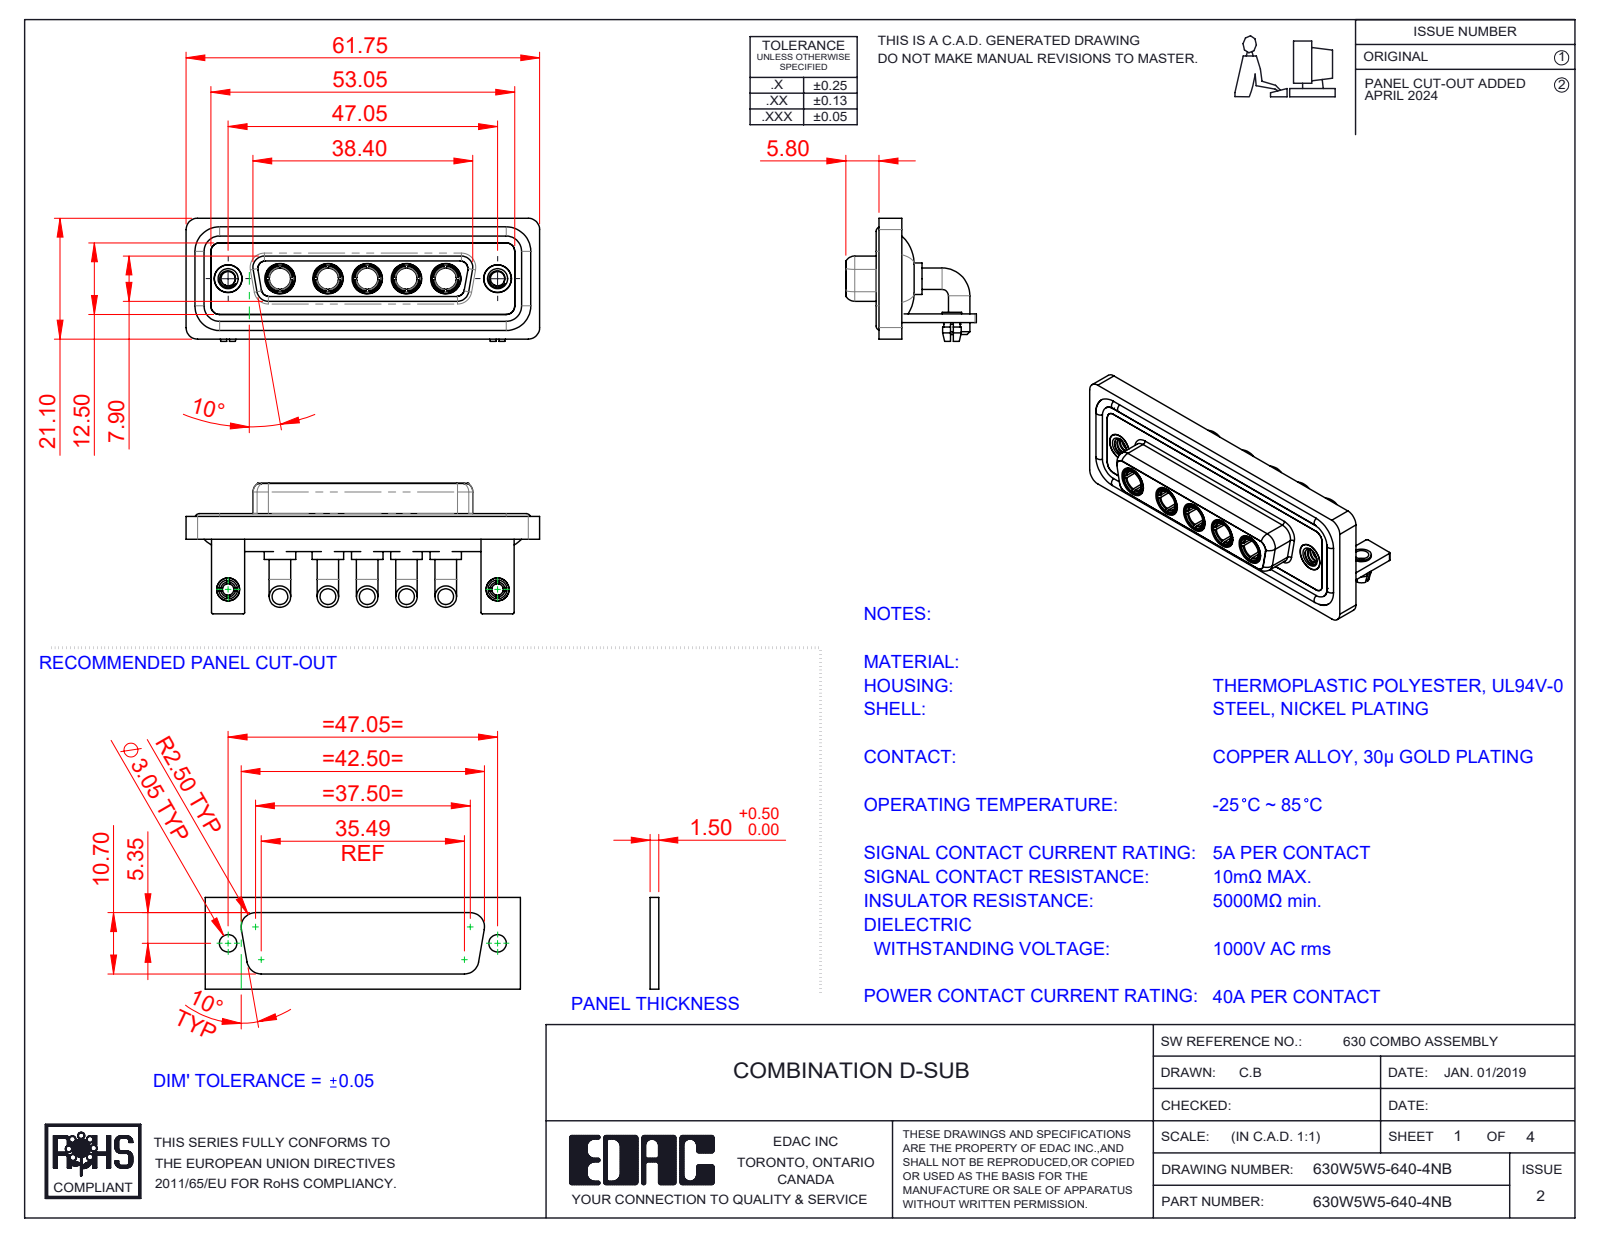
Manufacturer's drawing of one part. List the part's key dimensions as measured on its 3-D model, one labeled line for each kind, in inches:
Part name (STEP PRODUCT): Power Socket_40A RA; 630W5W5-640-4NB; 630Combo Board Lock_50 Contacts; 630Combo Threaded Rivet_A (+5 more)
STEP written by: SolidWorks 2023 (CONFIG_CONTROL_DESIGN)
Units: inches
Bodies: 21 solids, 910 faces (318 planar, 367 cylindrical, 225 other)
Overall size (bounding box): 2.431 × 0.898 × 0.846
Volume: 0.561 in³ · Surface area: 23.22 in²
Round holes (diameter × count): ⌀0.191 ×7, ⌀0.146 ×5, ⌀0.209 ×5, ⌀0.098 ×4, ⌀0.079 ×2, ⌀0.126 ×2, ⌀0.157 ×2, ⌀0.159 ×2, ⌀0.197 ×2
Round bosses / shafts (diameter × count): ⌀0.148 ×10, ⌀0.217 ×5, ⌀0.205 ×5, ⌀0.195 ×5, ⌀0.187 ×5, ⌀0.063 ×4, ⌀0.195 ×2, ⌀0.189 ×2
Partial cylindrical surfaces — rounded edges, fillets, slot ends (radius × count): R0.079 ×19, R0.059 ×18, R0.01 ×16, R0.053 ×8, R0.063 ×8, R0.02 ×5, R0.083 ×5, R0.024 ×4
Main face-to-face distances: 0.016, 0.071, 0.114, 0.146, 0.059, 0.161, 0.043, 0.055, 0.063, 0.098
Hole centre spacings: 0.27, 0.356, 1.496, 1.852, 0.27, 0.33, 0.54, 0.541
